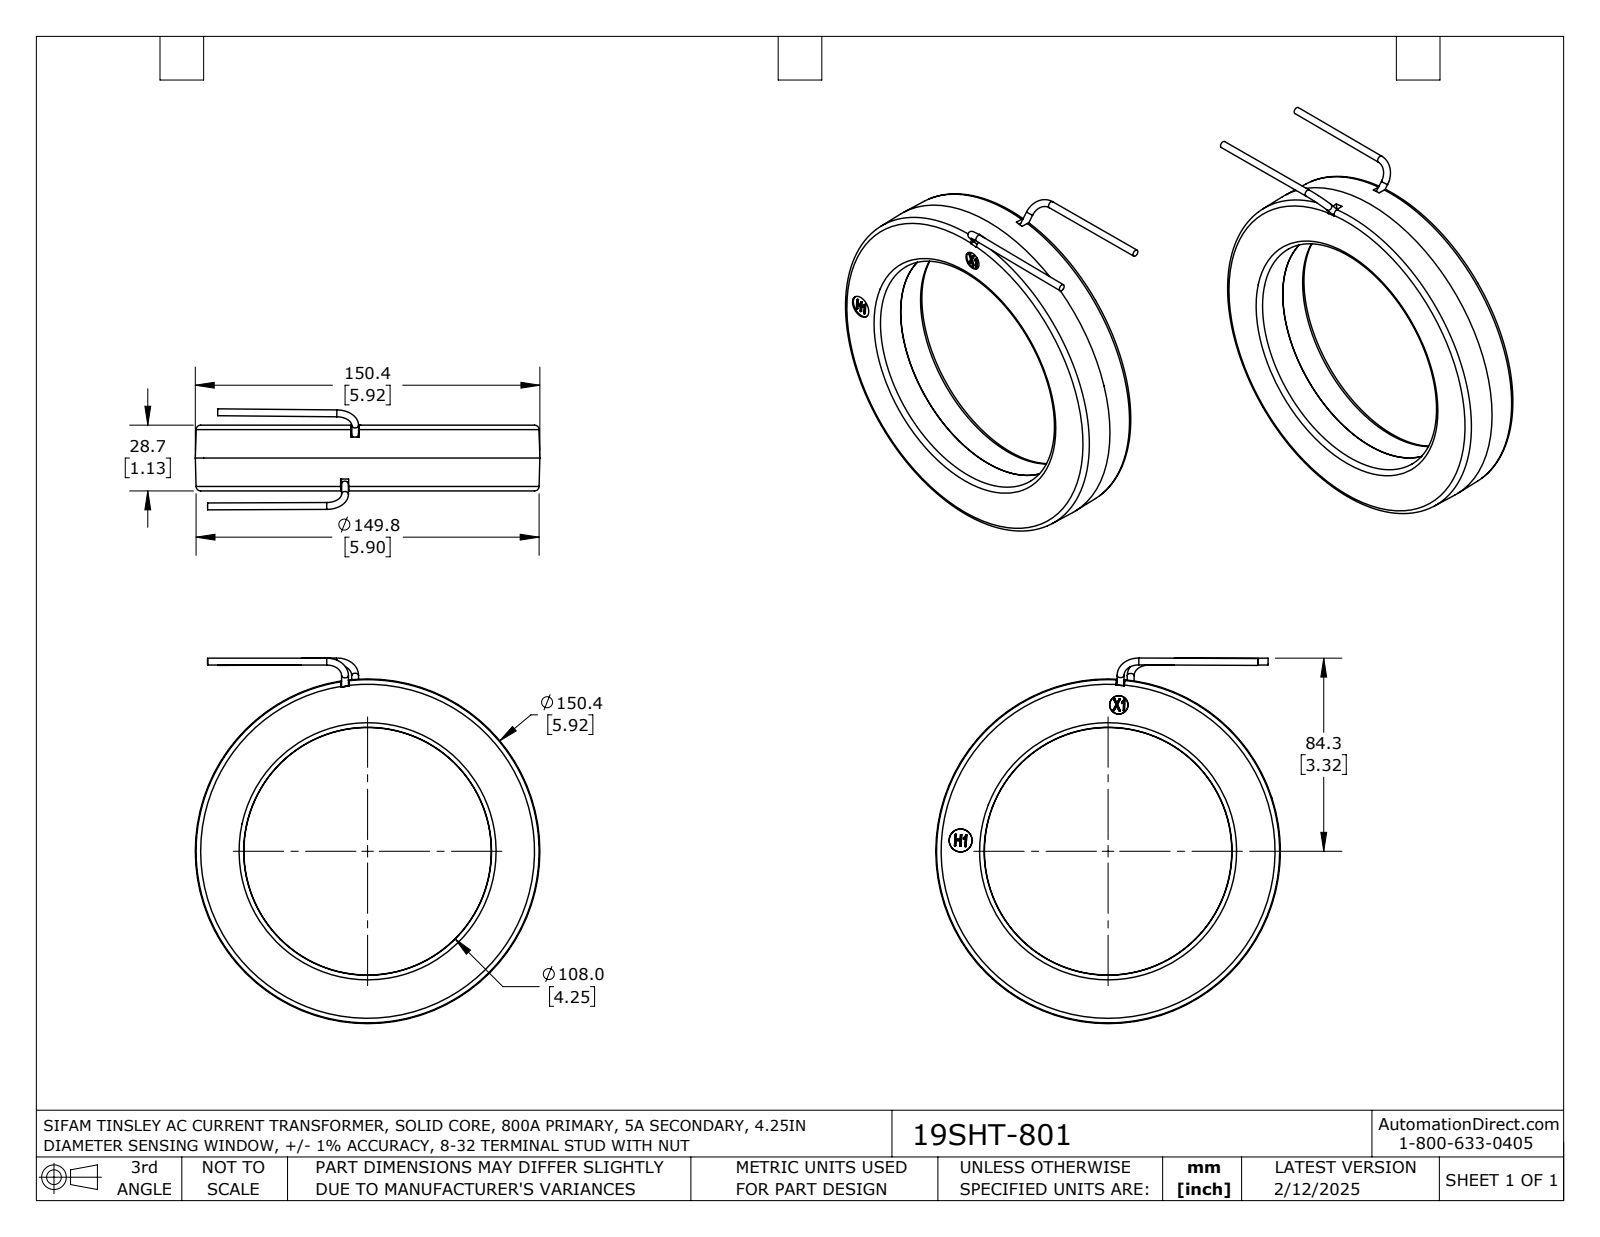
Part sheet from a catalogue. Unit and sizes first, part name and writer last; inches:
Units: inches
Overall size (bounding box): 6.611 × 6 × 2.909
Round bosses / shafts (diameter × count): ⌀0.394 ×2, ⌀0.236 ×2, ⌀0.217 ×2, ⌀0.158 ×2
Partial cylindrical surfaces — rounded edges, fillets, slot ends (radius × count): R0.11 ×12, R0.039 ×8, R0.098 ×8, R0.138 ×4, R0.012 ×2, R0.051 ×2, R0.054 ×2
Main face-to-face distances: 0.577, 0.573, 0.039, 1.15, 0.612, 0.616, 1.189, 6, 1.228, 6.17
Volume: 25.87 in³ · Surface area: 162.8 in²
Bodies: 1 solid, 412 faces (248 planar, 78 cylindrical, 86 other)
Part name (STEP PRODUCT): 19SHT-801
STEP written by: SolidWorks 2021 (AUTOMOTIVE_DESIGN)
